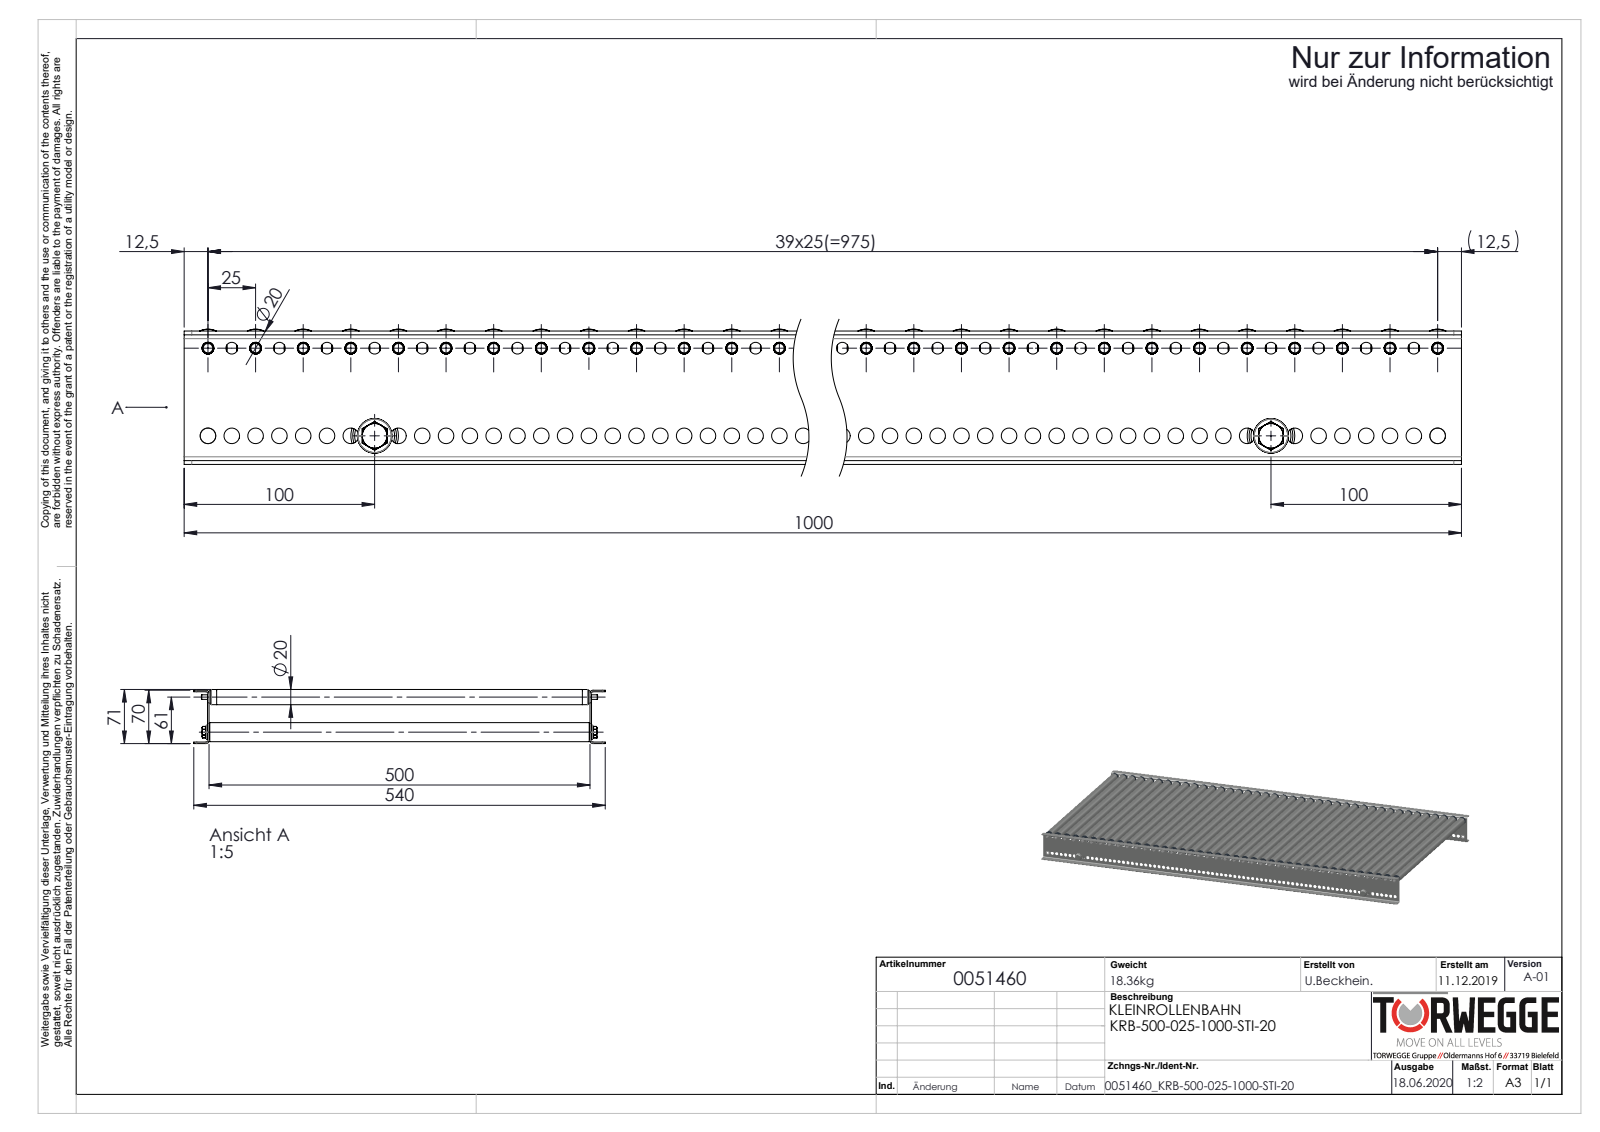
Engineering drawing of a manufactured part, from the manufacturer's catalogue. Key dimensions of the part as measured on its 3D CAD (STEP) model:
Part name (STEP PRODUCT): S100994_Sperrzahnschraube_M08x16-8.8-A2K; 0039777_Achse-Ø06-FA-KFG_L=520 fr D20; KUT50-20x1,5-STI-A6_FA-EL=KFG_S100911_KUT50-20x1-STI-A6-FA-EL=500; Profil_KRB-20x70x20x2_KFG_S100204_U-PROFIL-20-70-20-2-KRB-20-L=1000 (+4 more)
STEP written by: SolidWorks 2020 (AUTOMOTIVE_DESIGN)
Units: millimetres
Bodies: 92 solids, 7952 faces (2600 planar, 3008 cylindrical, 2344 other)
Overall size (bounding box): 1000 × 540 × 71
Volume: 2 293 000 mm³ · Surface area: 3 513 000 mm²
Round holes (diameter × count): ⌀6.2 ×79, ⌀8.2 ×79, ⌀6.1 ×40, ⌀14.2 ×40, ⌀17.2 ×40, ⌀18 ×40, ⌀6.8 ×2, ⌀21 ×2
Round bosses / shafts (diameter × count): ⌀20 ×40, ⌀19.9 ×40, ⌀18.1 ×40, ⌀17.8 ×40, ⌀16.5 ×40, ⌀6 ×40, ⌀25 ×2, ⌀8 ×2
Partial cylindrical surfaces — rounded edges, fillets, slot ends (radius × count): R4.05 ×40, R4 ×8, R2 ×4
Main face-to-face distances: 2, 502, 68, 500, 504, 66, 70, 492, 18, 30
Hole centre spacings: 12.5, 25, 37.5, 50, 62.5, 75, 87.5, 100
